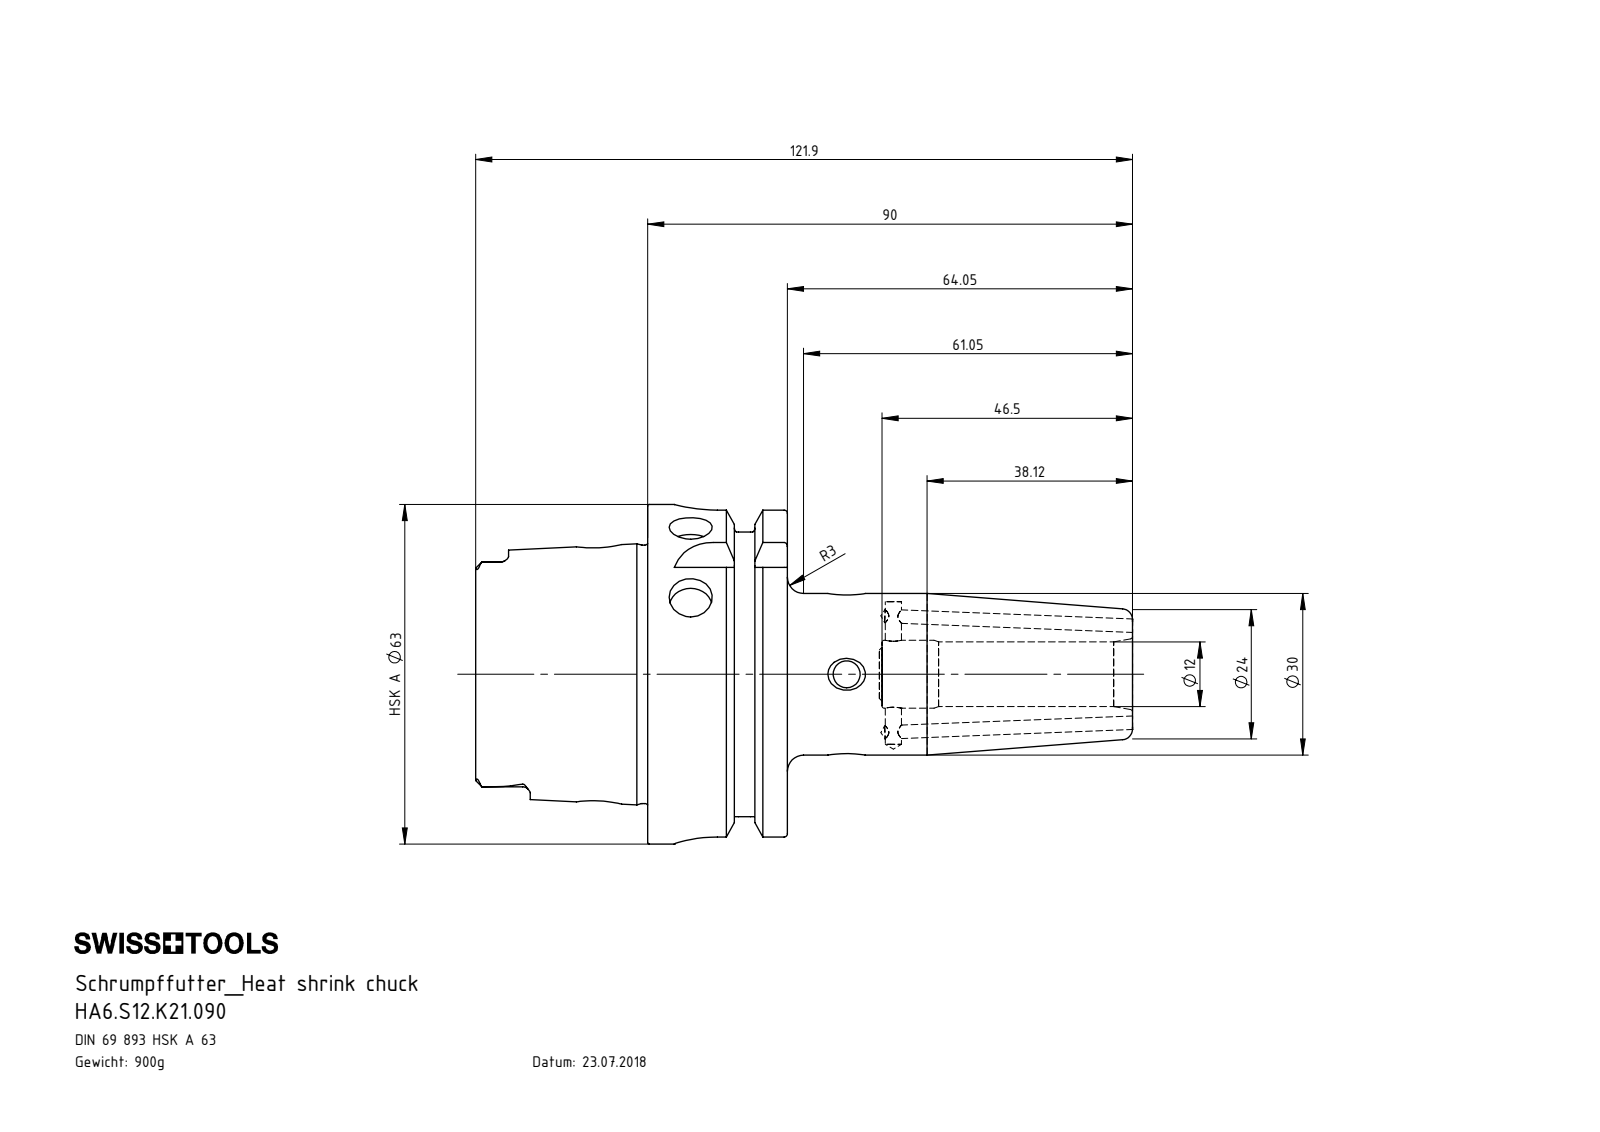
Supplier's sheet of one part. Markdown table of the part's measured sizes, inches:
| quantity | value |
| --- | --- |
| part name | HA6-S12.K21.090; ERU-CJ2.001.006; ERU-AN4.K01.020_A; HA6-S12.K21.090_C_Fertigbearbeitung |
| STEP written by | SolidWorks 2012 (CONFIG_CONTROL_DESIGN) |
| units | inches |
| bodies | 4 solids, 305 faces (101 planar, 83 cylindrical, 121 other) |
| overall size | 4.8 × 2.48 × 2.48 |
| volume | 6.993 in³ |
| surface area | 50.21 in² |
| round holes (diameter × count) | 0.197 × 3, 0.098 × 2, 0.315 × 2, 0.118 × 1, 0.295 × 1, 0.354 × 1, 0.394 × 1, 0.472 × 1, 0.496 × 1, 0.669 × 1, 0.748 × 1, 1.339 × 1 |
| round bosses / shafts (diameter × count) | 0.118 × 2, 2.48 × 1, 2.163 × 1, 1.887 × 1, 1.181 × 1, 0.394 × 1 |
| partial cylindrical surfaces (radius × count) | 0.055 × 6, 0.113 × 4, 0.315 × 4 |
| main face-to-face distances | 1.022, 0.63, 0.392, 1.256, 1.648, 2.278, 2.079, 0.858, 0.467, 2.114 |
| hole center spacings | 0.341, 1.179, 1.809, 2.15 |
